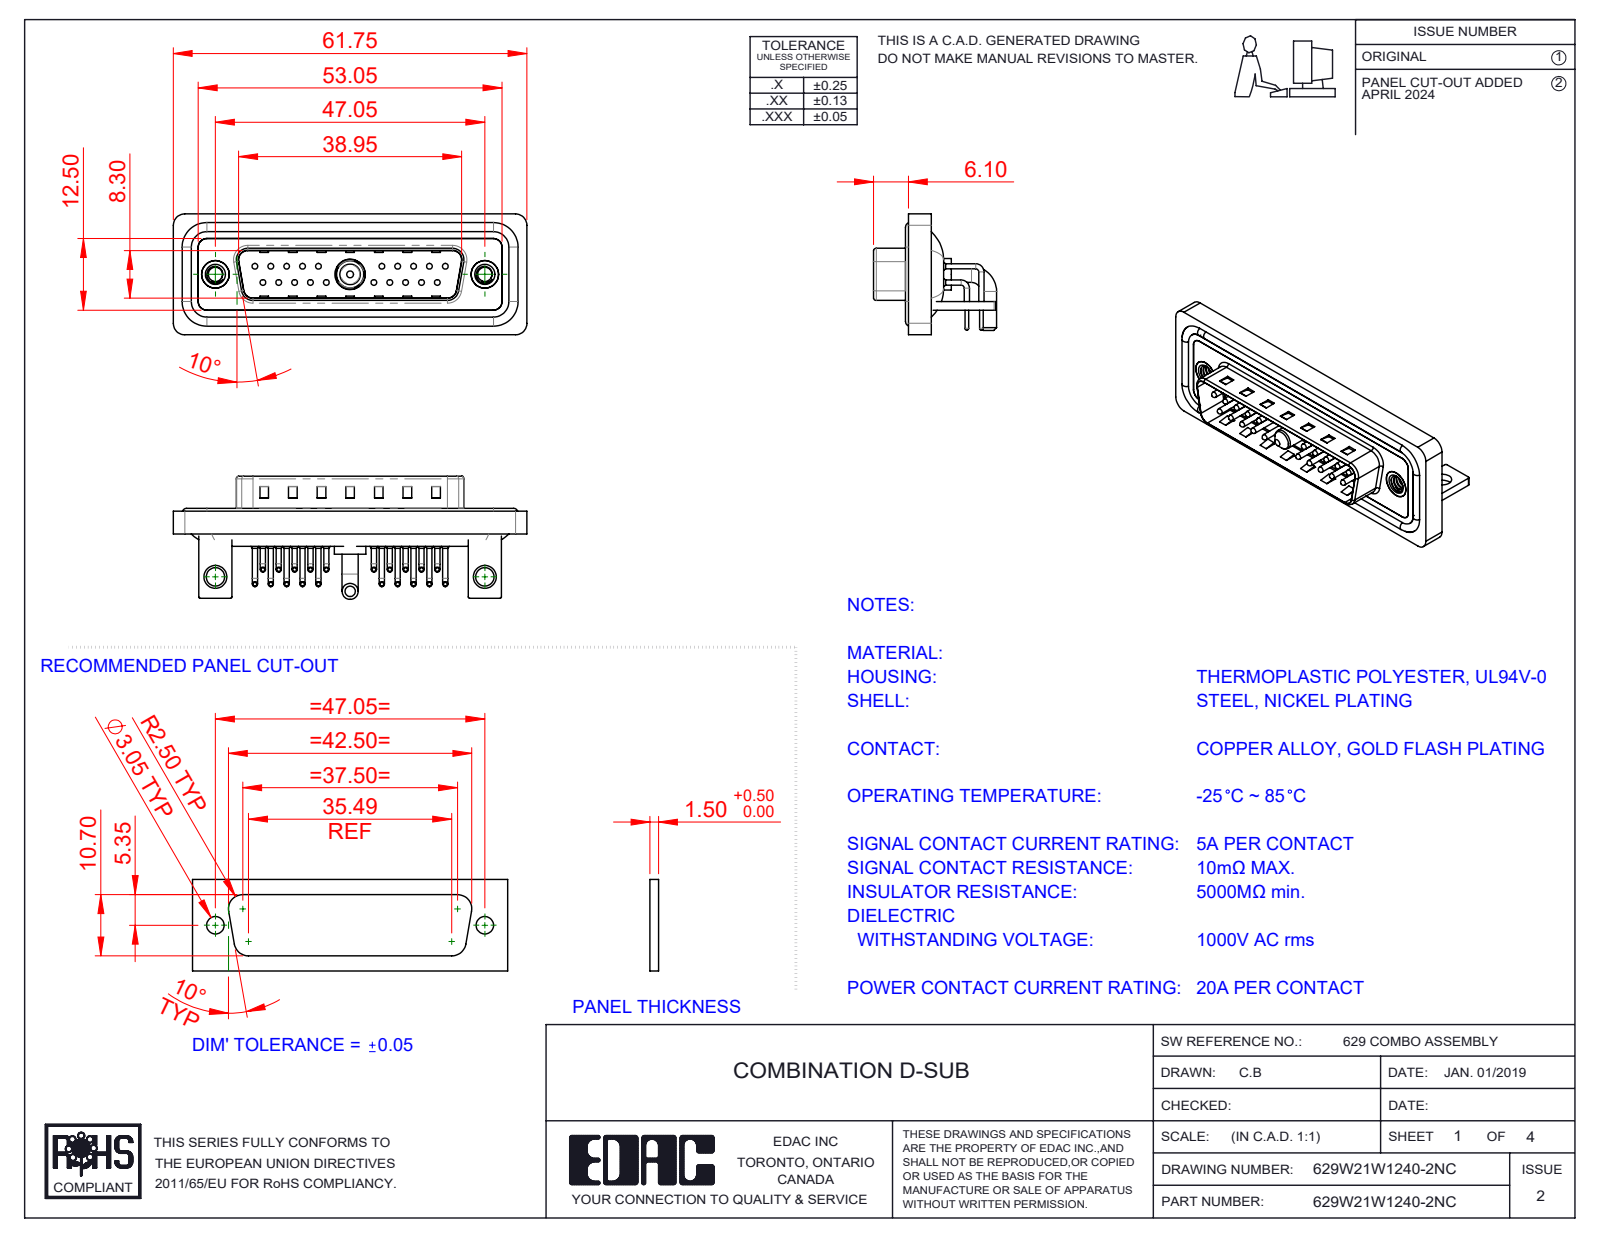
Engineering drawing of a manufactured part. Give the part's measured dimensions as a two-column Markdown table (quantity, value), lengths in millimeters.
| quantity | value |
| --- | --- |
| part name | 629W21W1240-2NC; 629Combo Housing_21W1; Power Pin_20A RA; 629Combo Shell Front_25 Contacts (+6 more) |
| STEP written by | SolidWorks 2023 (CONFIG_CONTROL_DESIGN) |
| units | millimeters |
| bodies | 31 solids, 2764 faces (1519 planar, 947 cylindrical, 298 other) |
| overall size | 61.75 × 21.5 × 21.1 |
| volume | 7 690 mm³ |
| surface area | 13 309 mm² |
| round holes (diameter × count) | 0.75 × 20, 1.6 × 20, 2 × 20, 2.5 × 2, 3.2 × 2, 4 × 2, 4.8 × 2, 5 × 2, 4.85 × 1, 5.3 × 1 |
| round bosses / shafts (diameter × count) | 0.9 × 40, 1.5 × 20, 1 × 20, 0.65 × 20, 1.6 × 4, 4.9 × 2, 2.8 × 2, 5.5 × 1 |
| partial cylindrical surfaces (radius × count) | 1.01 × 20, 2 × 19, 1.5 × 18, 0.25 × 16, 0.5 × 9, 1.6 × 8, 0.6 × 4, 0.65 × 4 |
| main face-to-face distances | 0.4, 0.8, 2.1, 2.9, 1.5, 1.1, 4.1, 1.6, 4.5, 3.7 |
| hole center spacings | 3.16, 2.77, 5.54, 8.31, 5.04, 19.39, 20.97, 22.16 |
